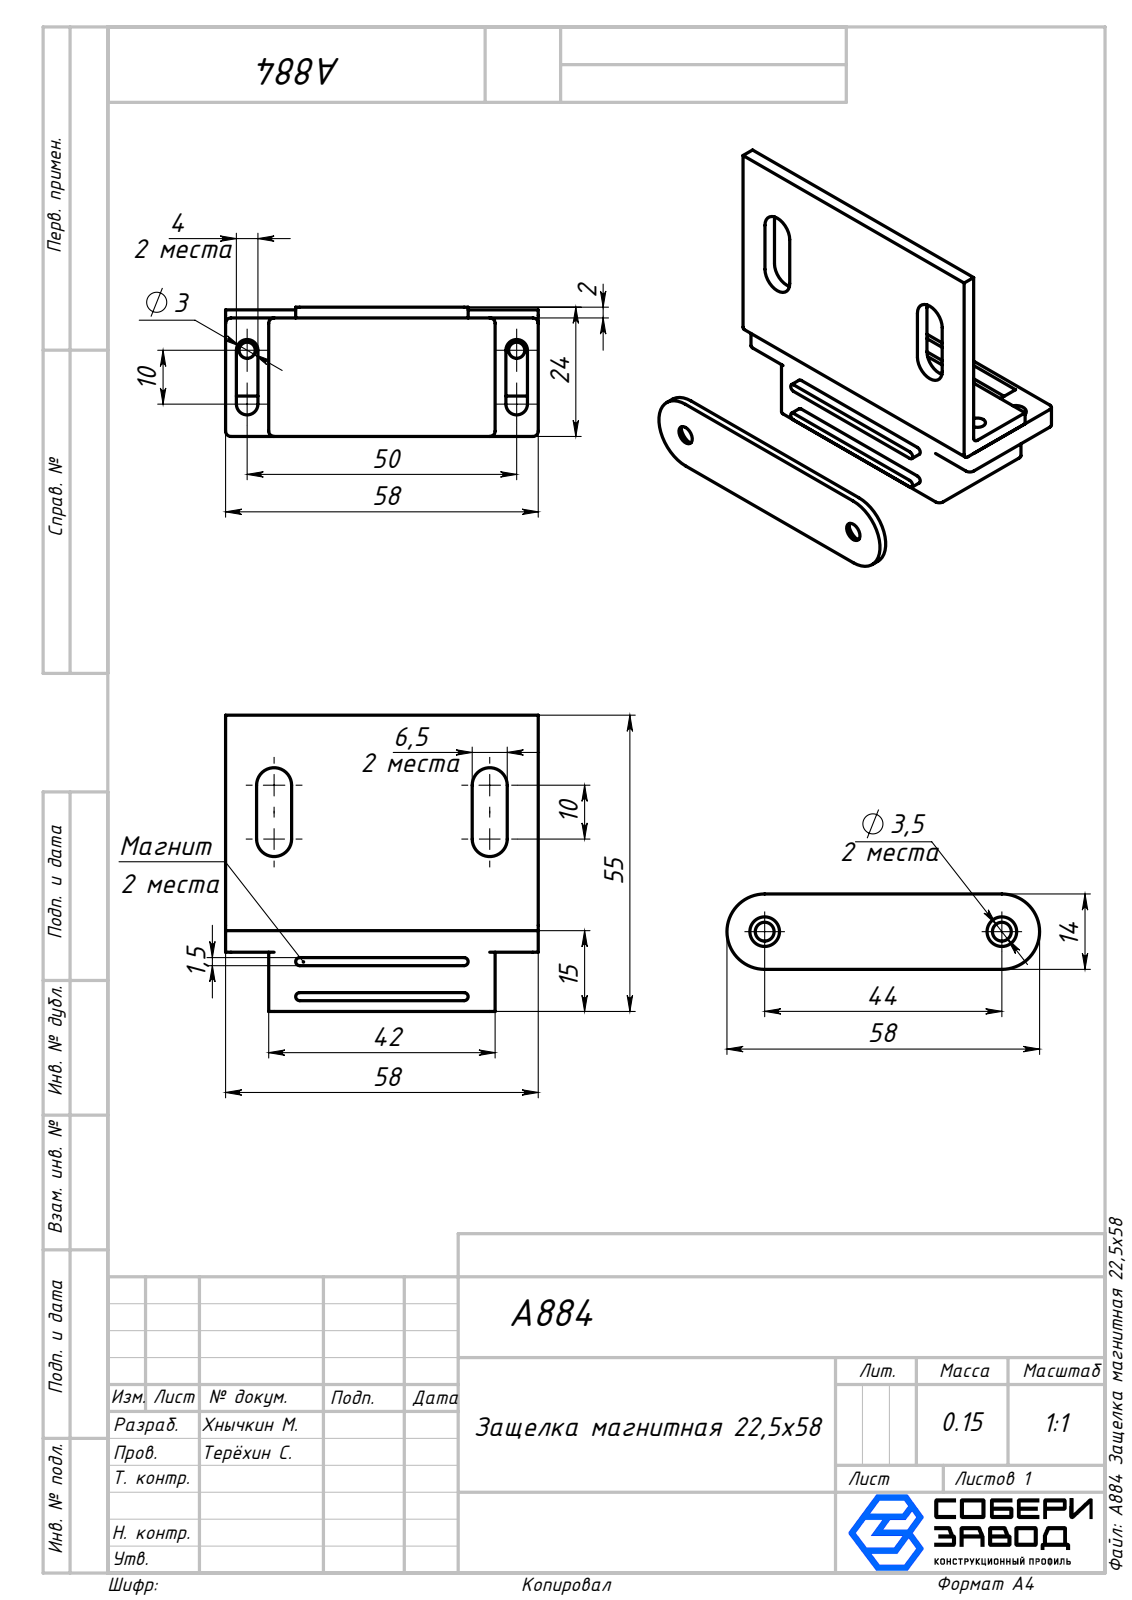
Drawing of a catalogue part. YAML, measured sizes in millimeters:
part_name: "A884 Защелка магнитная 22,5х58_00; Крепление на дверь_00; Крепление для магнита_00; A884 Защелка магнитная 22,5х58"
step_written_by: "SolidWorks 2025 (AUTOMOTIVE_DESIGN)"
units: millimeters
bodies: {solids: 3, faces: 79, planar: 41, cylindrical: 34, other: 4}
overall_size: [58.05, 56, 45.62]
volume: 20969
surface_area: 13510
round_holes:
  - {diameter: 3, count: 2}
  - {diameter: 3.5, count: 2}
partial_cylinders:
  - {radius: 1, count: 10}
  - {radius: 0.75, count: 4}
  - {radius: 2, count: 4}
  - {radius: 3.25, count: 4}
  - {radius: 7, count: 2}
face_to_face_distances: [2.5, 1.5, 22.12, 1, 3, 15, 12, 21, 24.62, 23.12]
hole_center_spacings: [44, 50]
